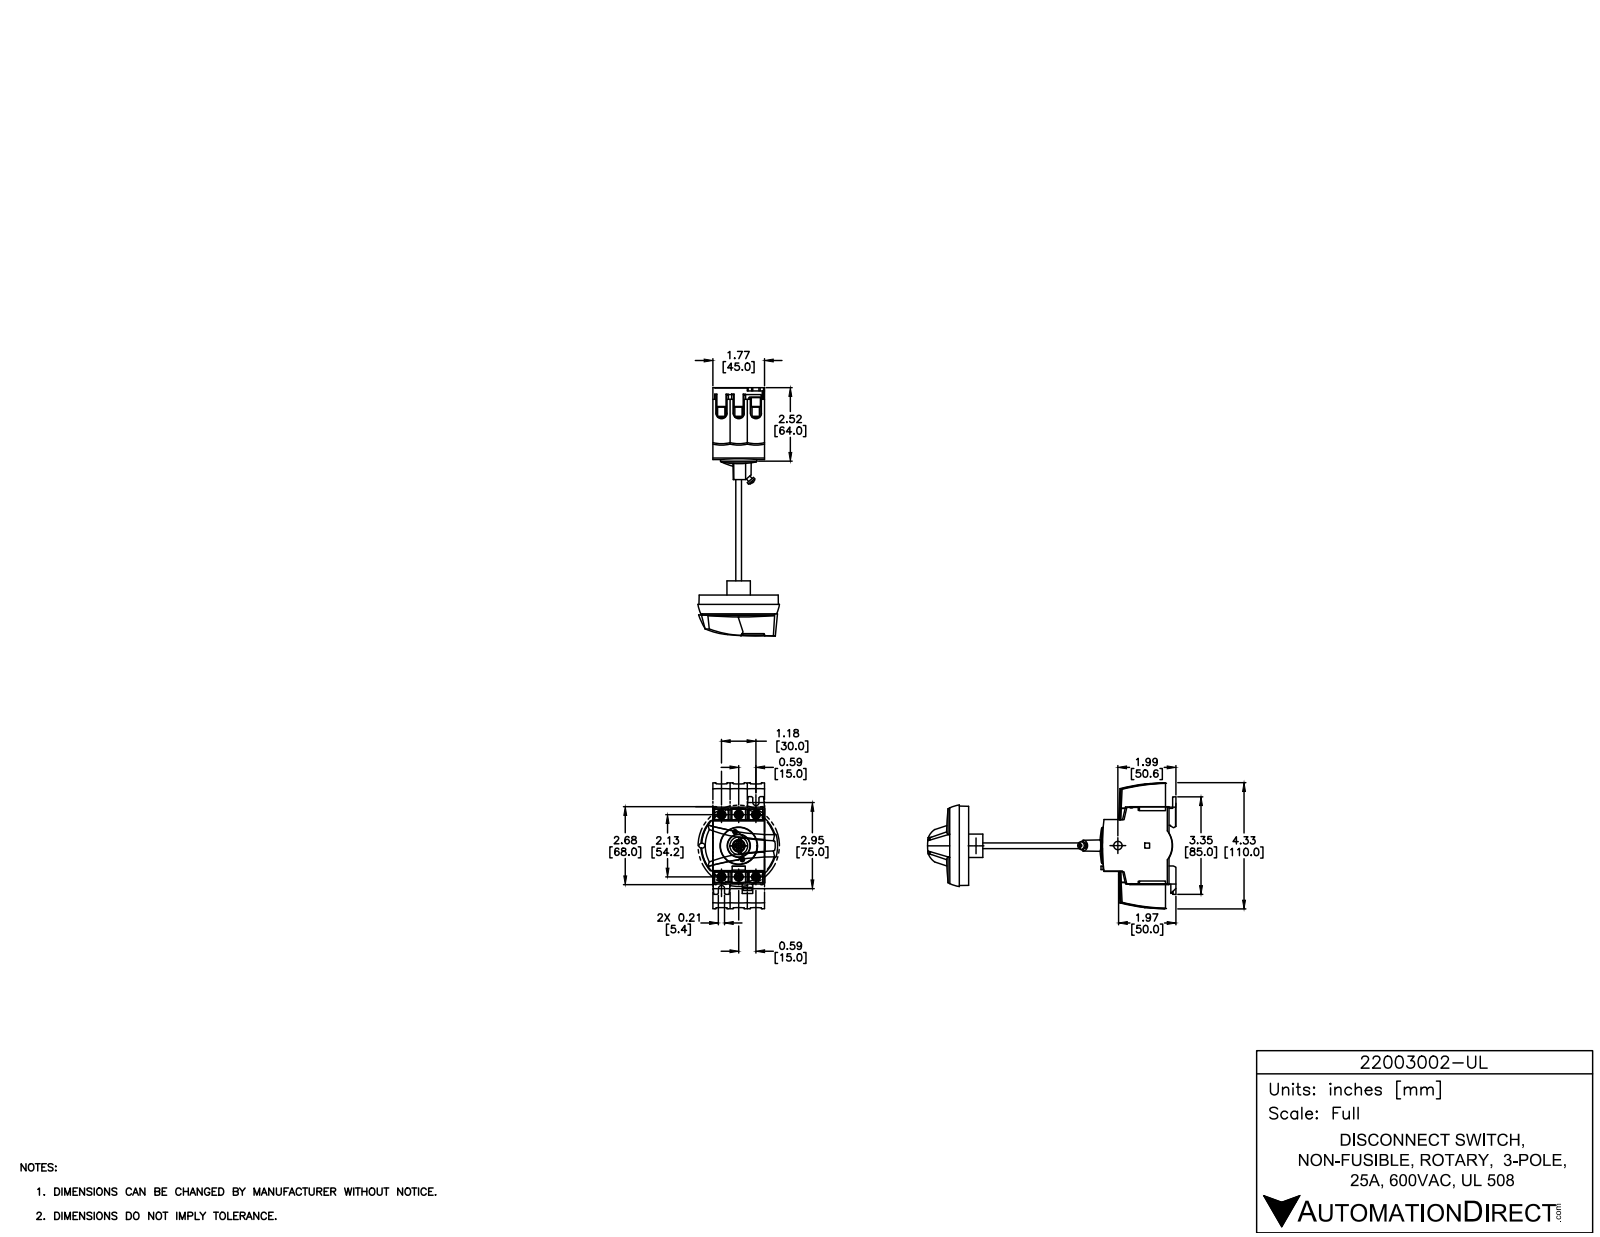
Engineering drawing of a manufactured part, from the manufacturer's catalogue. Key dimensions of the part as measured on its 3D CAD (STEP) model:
Part name (STEP PRODUCT): 22003002-UL
STEP written by: SolidWorks 2015 (AUTOMOTIVE_DESIGN)
Units: inches
Bodies: 1 solid, 463 faces (389 planar, 50 cylindrical, 24 other)
Overall size (bounding box): 3.346 × 2.571 × 1.772
Volume: 9.498 in³ · Surface area: 40.23 in²
Round holes (diameter × count): ⌀0.26 ×6, ⌀0.283 ×1, ⌀1.244 ×1
Partial cylindrical surfaces — rounded edges, fillets, slot ends (radius × count): R0.012 ×13, R0.02 ×5, R0.165 ×4, R0.039 ×3, R0.106 ×2, R0.13 ×1, R0.354 ×1, R0.37 ×1
Main face-to-face distances: 1.772, 0.433, 2.205, 2.157, 2.638, 2.28, 0.591, 2.591, 0.047, 0.386
Hole centre spacings: 0.591, 1.219, 2.214, 2.134, 1.067, 1.181, 2.439
